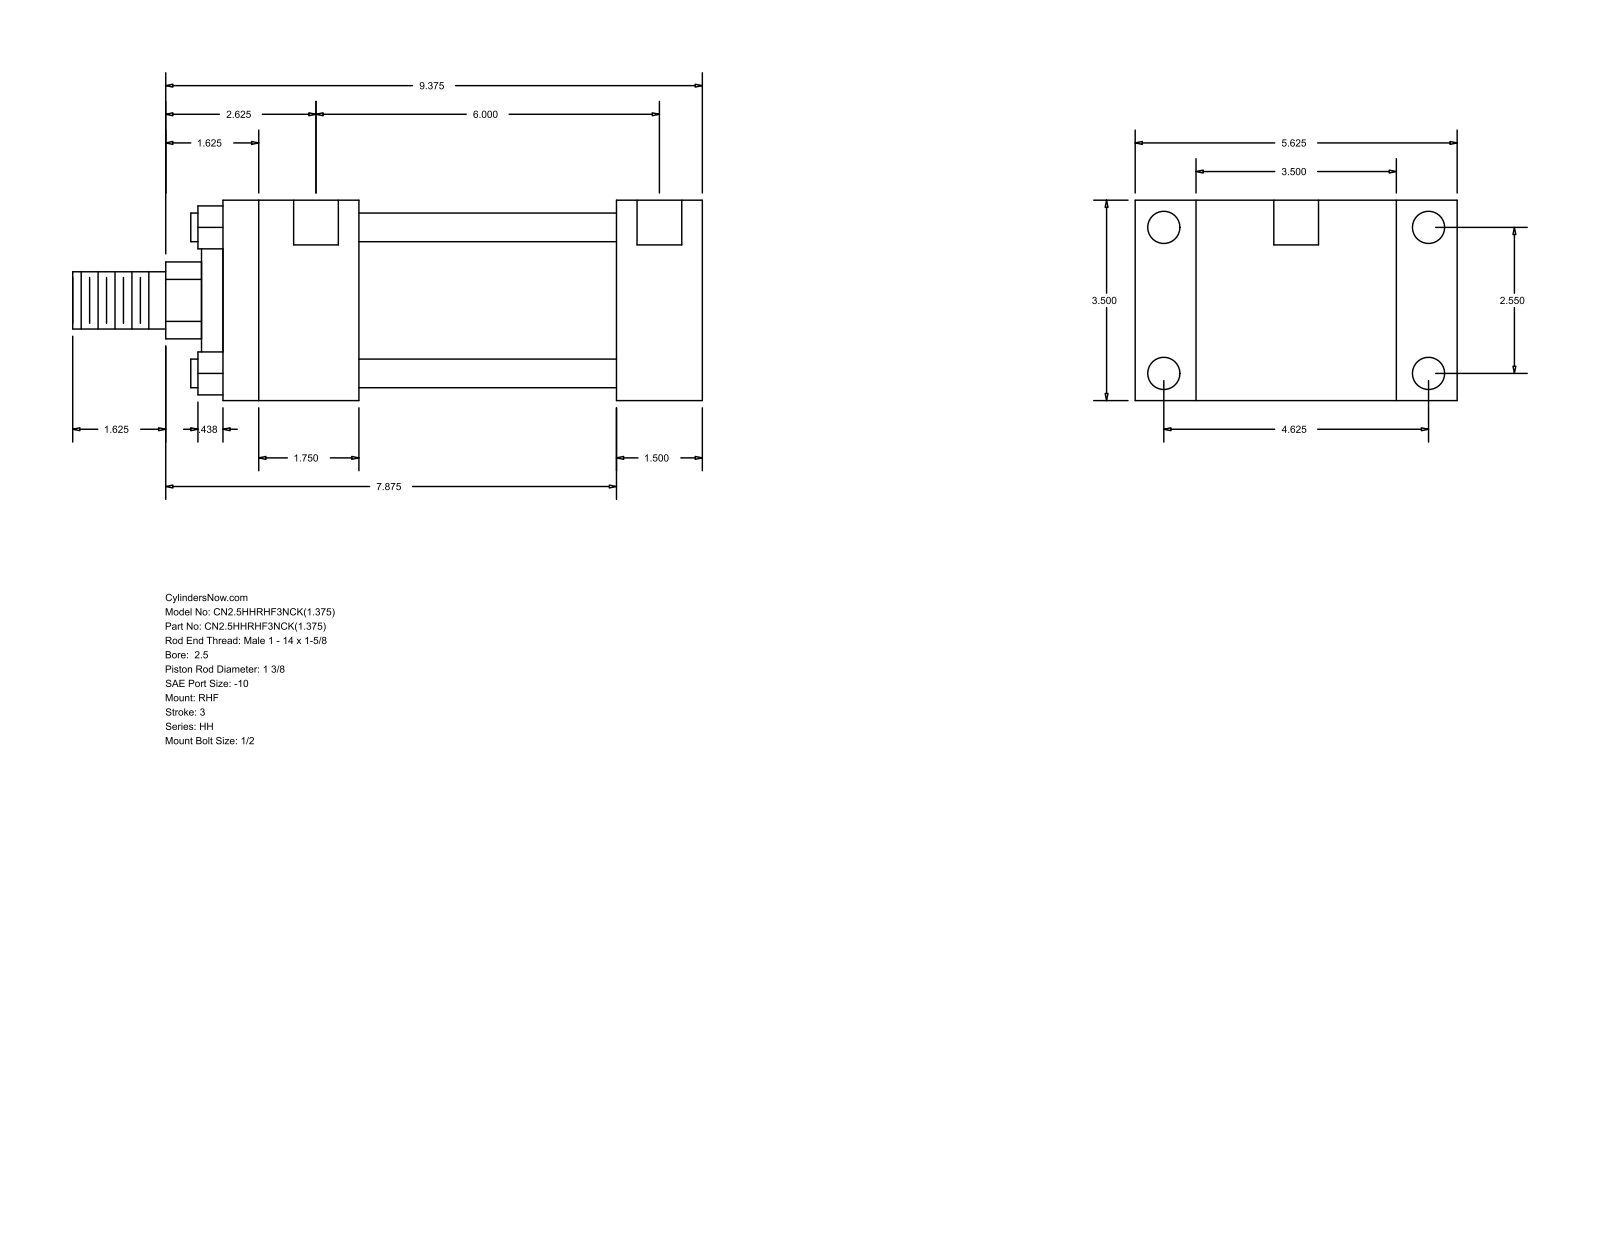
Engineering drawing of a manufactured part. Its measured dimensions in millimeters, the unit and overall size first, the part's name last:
Units: millimetres
Overall size (bounding box): 279.4 × 142.88 × 88.9
Round holes (diameter × count): ⌀5.56 ×4, ⌀14.3 ×4, ⌀19.84 ×2
Round bosses / shafts (diameter × count): ⌀12.7 ×4, ⌀73.03 ×1, ⌀50.8 ×1, ⌀34.92 ×1, ⌀25.4 ×1
Partial cylindrical surfaces — rounded edges, fillets, slot ends (radius × count): R17.06 ×1
Main face-to-face distances: 88.9, 38.09, 26.99, 115.89, 174.63, 212.72, 142.88, 60.32, 114.31, 152.4
Hole centre spacings: 64.76, 117.48, 134.15, 155.57, 1.58, 1.59, 152.4, 153.98
Bodies: 0 solids, 88 faces (60 planar, 28 cylindrical, 0 other)
Part name (STEP PRODUCT): HH_RHF__0250_1.375
STEP written by: GSSL Pune (CONFIG_CONTROL_DESIGN)
